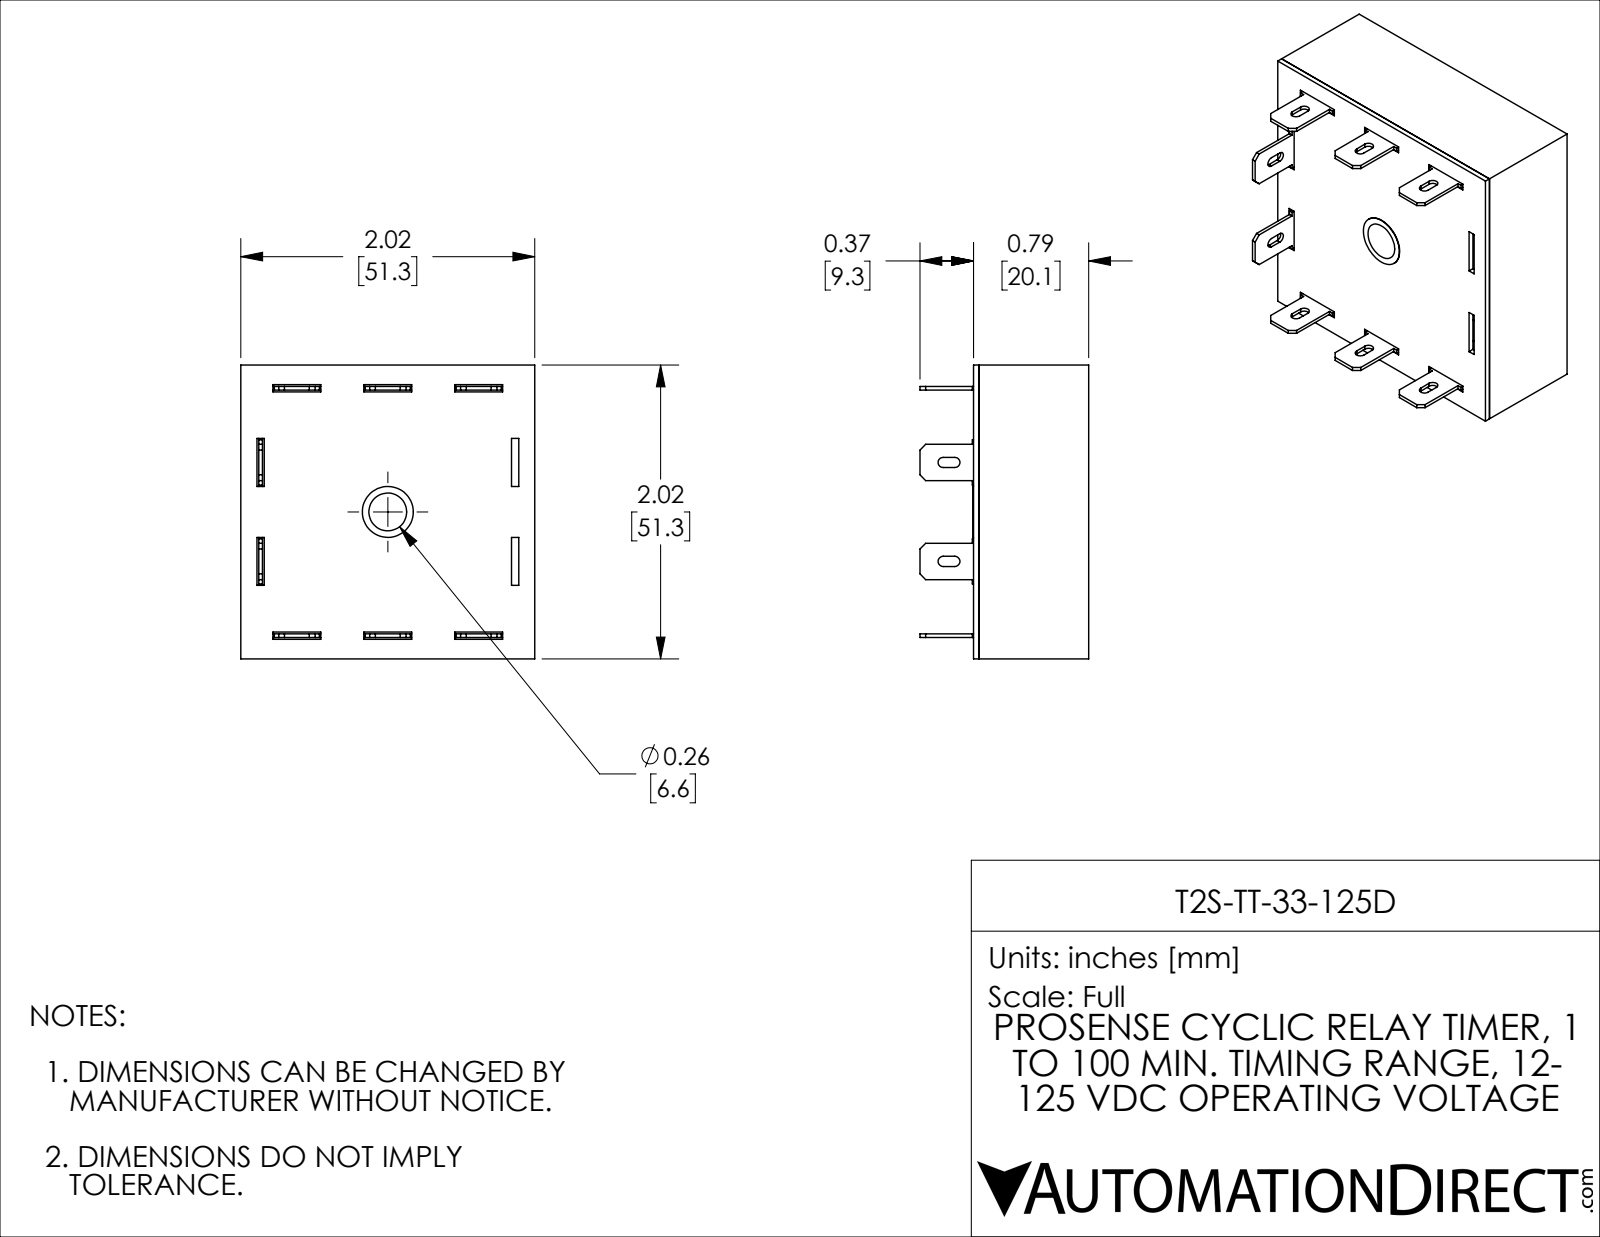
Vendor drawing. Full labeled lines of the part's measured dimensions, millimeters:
Part name (STEP PRODUCT): T2S-TT-33-125D
STEP written by: SolidWorks 2021 (CONFIG_CONTROL_DESIGN)
Units: millimetres
Bodies: 10 solids, 256 faces (234 planar, 20 cylindrical, 2 other)
Overall size (bounding box): 51.31 × 51.31 × 29.46
Volume: 11 042 mm³ · Surface area: 22 819 mm²
Round holes (diameter × count): ⌀8.89 ×1
Partial cylindrical surfaces — rounded edges, fillets, slot ends (radius × count): R0.89 ×10
Main face-to-face distances: 1.14, 50.16, 19.15, 20.12, 0.97, 18.01, 18.98, 51.3, 49.02, 3.74
